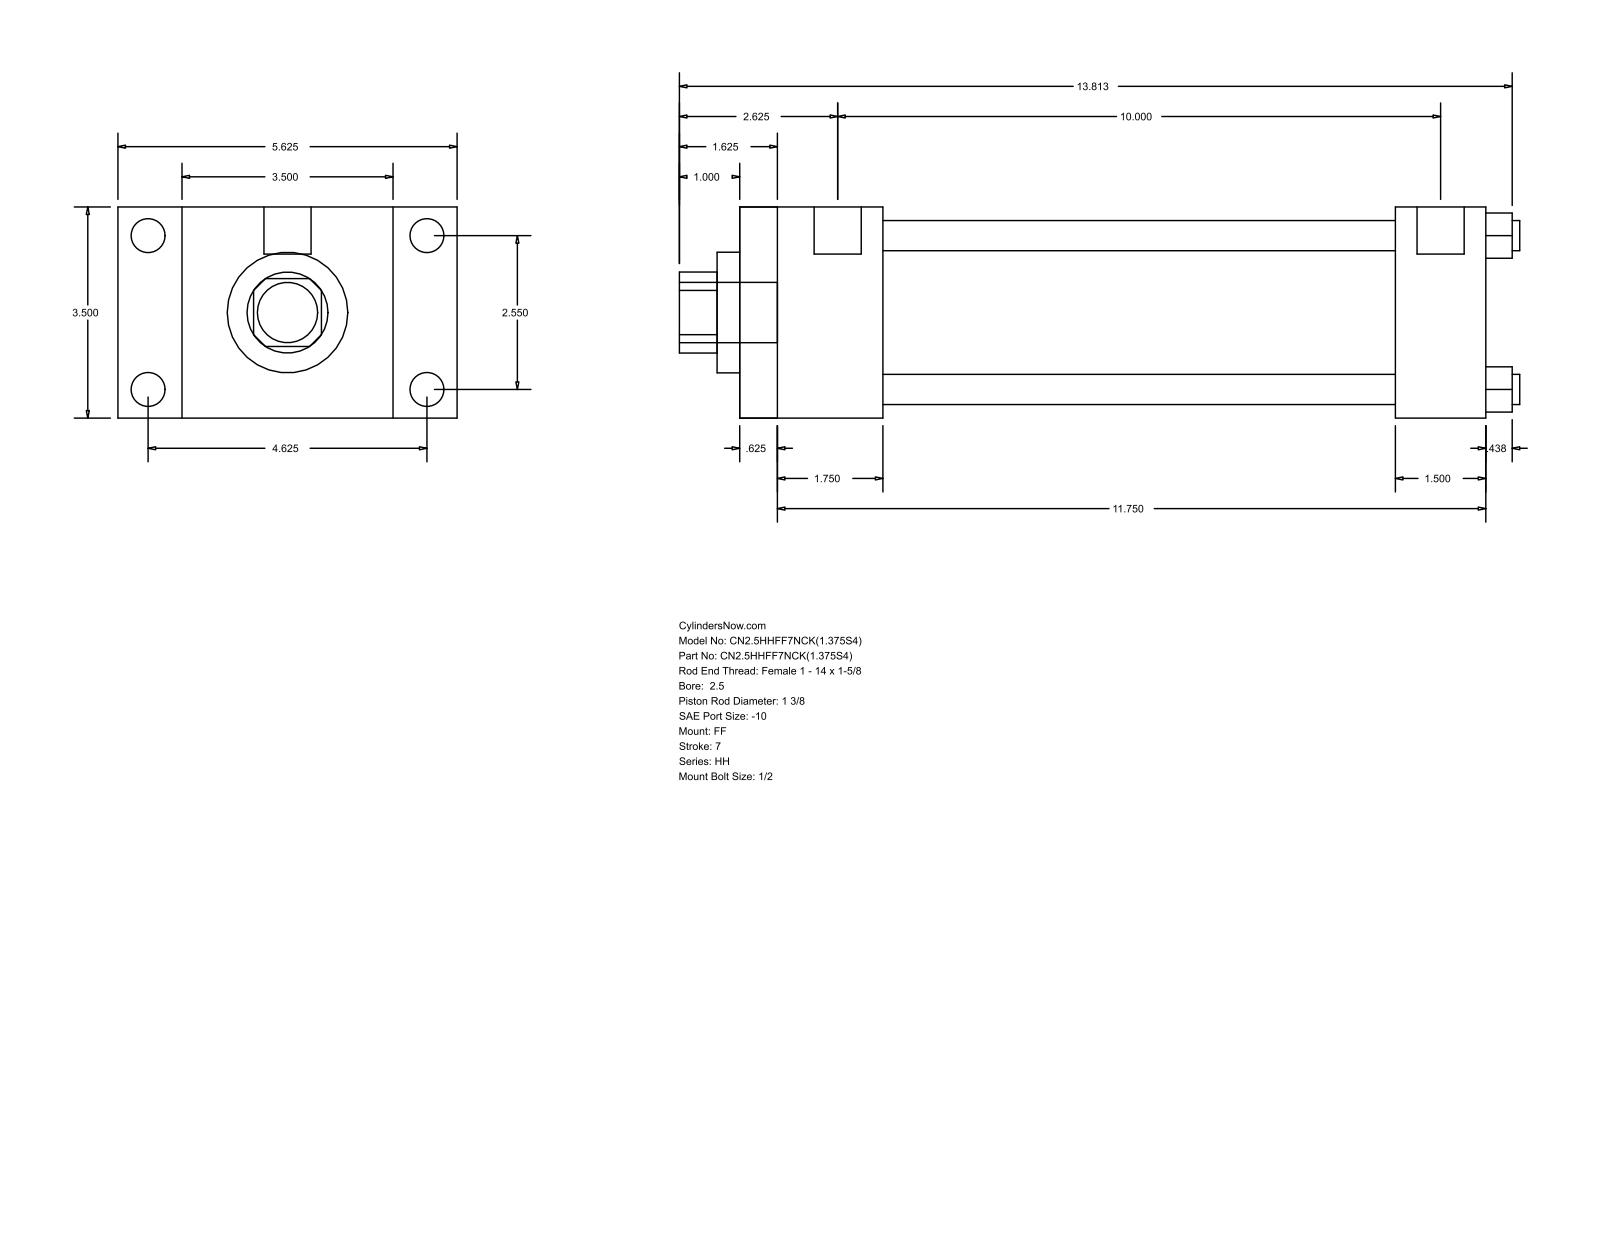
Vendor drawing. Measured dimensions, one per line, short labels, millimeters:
name: HH_FF__0250_1.375
written by: GSSL Pune (CONFIG_CONTROL_DESIGN)
unit: mm
bodies: 0 solids, 92 faces (64 planar, 28 cylindrical, 0 other)
size: 354.01 × 142.88 × 88.9
holes: 4× ⌀12.7, 1× ⌀34.92, 1× ⌀50.8, 1× ⌀73.03
bosses: 4× ⌀14.3, 4× ⌀5.56, 2× ⌀19.84, 1× ⌀25.4
rounds: 1× R17.06
face distances: 88.9, 314.33, 15.87, 298.46, 60.32, 44.45, 254.01, 276.22, 260.35, 215.9
hole spacings: 45.79, 64.76, 91.58
